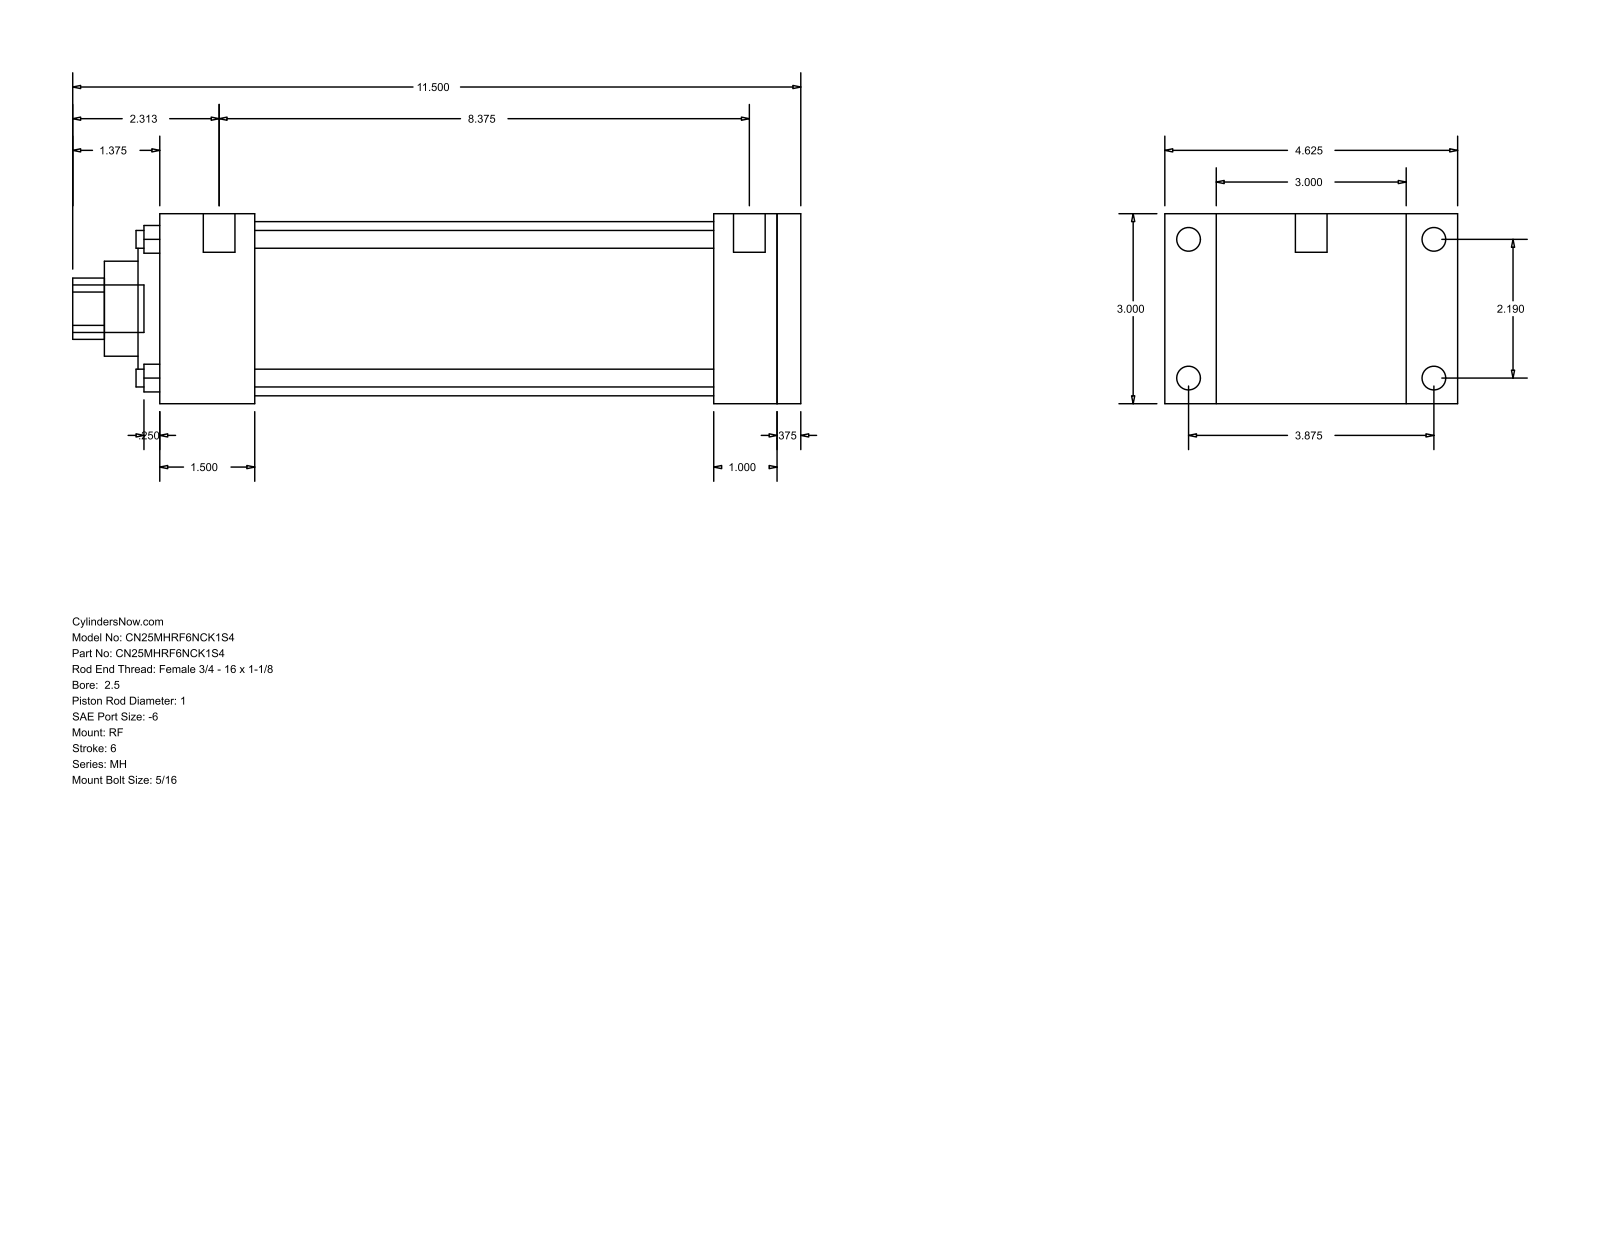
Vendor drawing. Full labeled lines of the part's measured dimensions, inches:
Part name (STEP PRODUCT): MH_RF__0250_1
STEP written by: GSSL Pune (CONFIG_CONTROL_DESIGN)
Units: inches
Bodies: 0 solids, 94 faces (65 planar, 29 cylindrical, 0 other)
Overall size (bounding box): 11.5 × 4.625 × 3
Round holes (diameter × count): ⌀0.281 ×4, ⌀1 ×1, ⌀1.5 ×1, ⌀2.375 ×1, ⌀2.75 ×1
Round bosses / shafts (diameter × count): ⌀0.375 ×4, ⌀0.219 ×4, ⌀0.5 ×2, ⌀0.75 ×1
Partial cylindrical surfaces — rounded edges, fillets, slot ends (radius × count): R0.484 ×1
Main face-to-face distances: 3, 0.375, 10.125, 9.75, 1.375, 1, 8.75, 1.5, 7.25, 8.25
Hole centre spacings: 1.548, 2.19, 3.097
